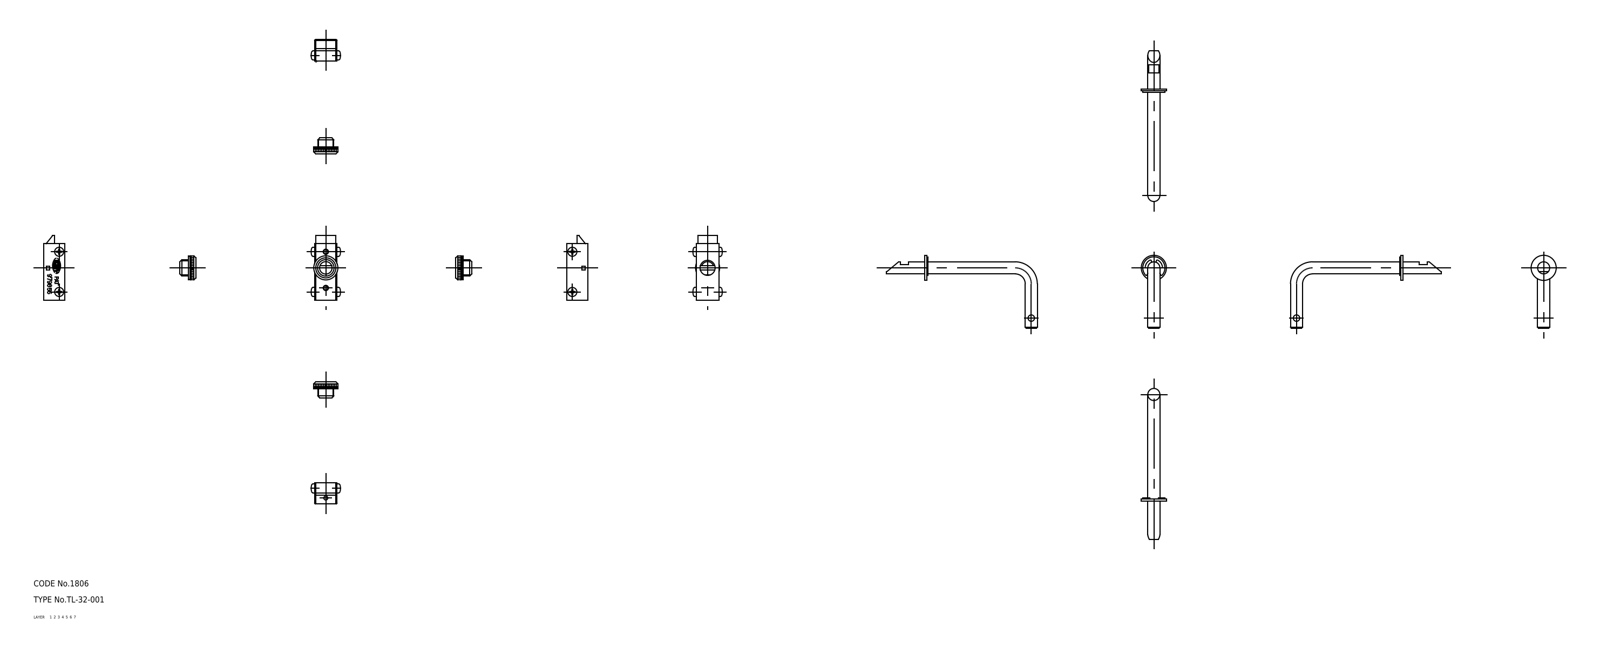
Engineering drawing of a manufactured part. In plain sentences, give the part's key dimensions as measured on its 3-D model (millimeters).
The part is named "retainer; packing; screw; washer (+7 more)". Its 3-D file was written by "CADfix (AUTOMOTIVE_DESIGN)". It is 13 solids with 278 faces: 0 planar, 0 cylindrical and 278 other. Overall it measures 109.4 by 46 by 14.56 millimeters. Its volume is 5 219 cubic millimeters and its surface area 6 856 square millimeters.
